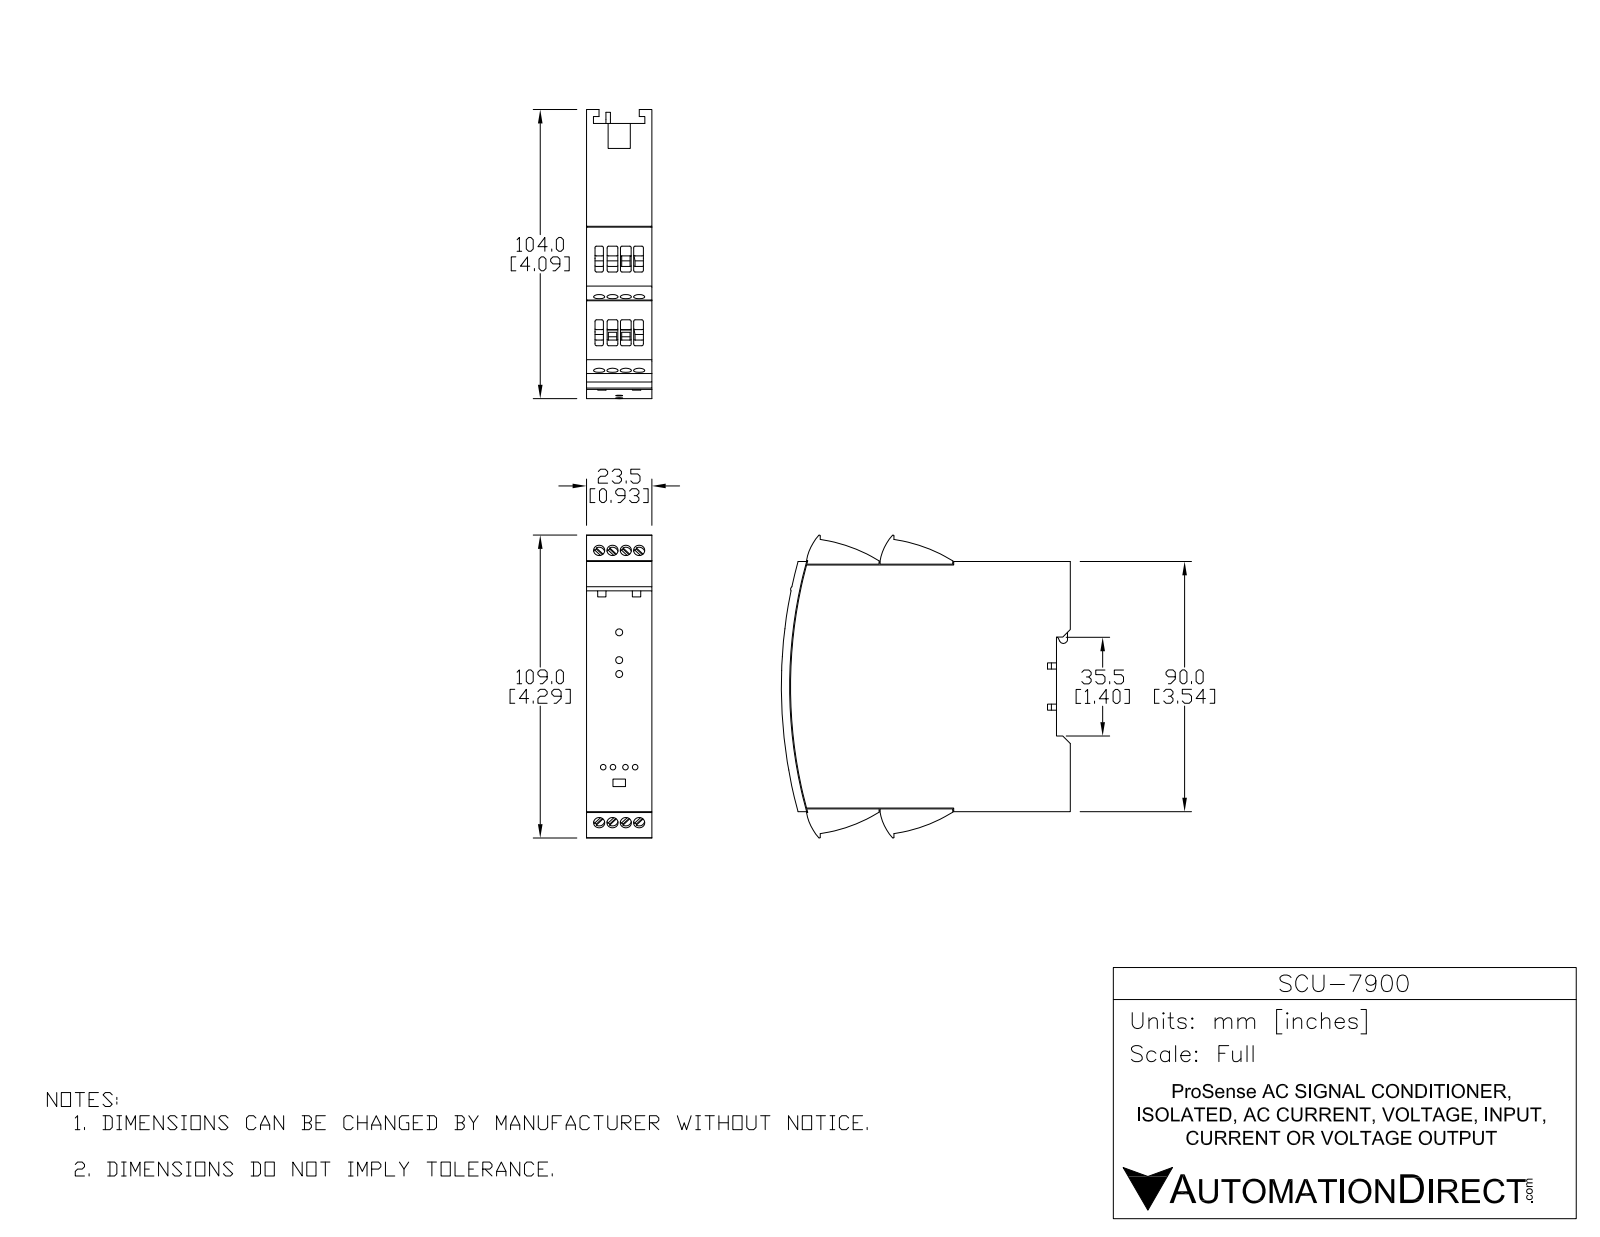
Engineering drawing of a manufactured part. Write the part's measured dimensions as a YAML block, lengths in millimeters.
part_name: "SCU-7900"
step_written_by: "SolidWorks 2017 (AUTOMOTIVE_DESIGN)"
units: millimeters
bodies: {solids: 1, faces: 913, planar: 549, cylindrical: 188, other: 176}
overall_size: [109, 104, 23.5]
volume: 216810
surface_area: 32765
round_holes:
  - {diameter: 4, count: 16}
  - {diameter: 2.3, count: 4}
  - {diameter: 2.5, count: 1}
partial_cylinders:
  - {radius: 0.5, count: 67}
  - {radius: 1, count: 9}
  - {radius: 0.3, count: 4}
  - {radius: 18.44, count: 4}
  - {radius: 55.25, count: 4}
  - {radius: 171.75, count: 2}
  - {radius: 1.08, count: 1}
  - {radius: 1.5, count: 1}
face_to_face_distances: [23.5, 90, 2.5, 5, 4.8, 4.5, 16.5, 3.05, 20.45, 2]
hole_center_spacings: [4.8, 11.02, 9.6, 9.92, 13.81, 14.4, 17.49, 5.3]
